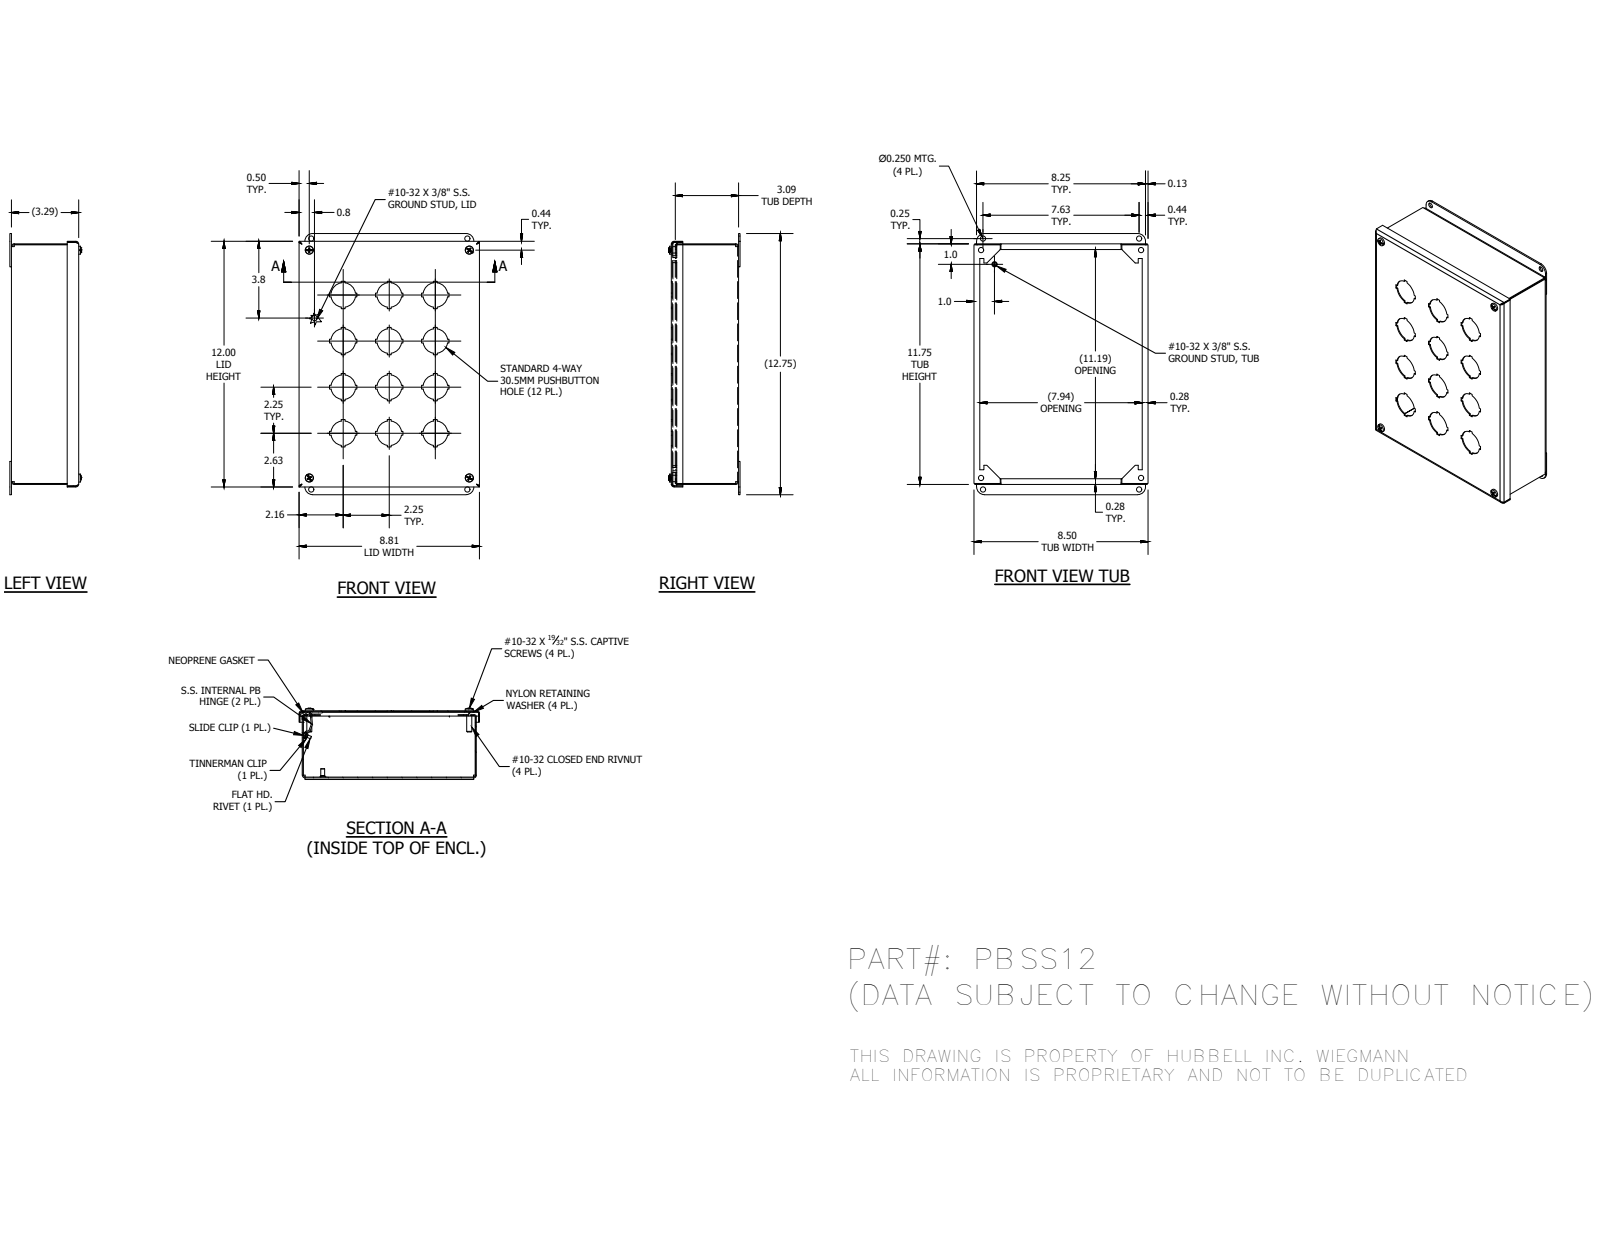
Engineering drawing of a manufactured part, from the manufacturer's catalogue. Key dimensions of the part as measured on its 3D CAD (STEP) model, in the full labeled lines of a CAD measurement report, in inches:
Part name (STEP PRODUCT): PBSS12LID; 37210; 39077; PBSS12BKP (+8 more)
STEP written by: Autodesk Inventor 2016 (AUTOMOTIVE_DESIGN)
Units: inches
Bodies: 25 solids, 841 faces (553 planar, 180 cylindrical, 108 other)
Overall size (bounding box): 12.75 × 8.813 × 3.481
Volume: 22.16 in³ · Surface area: 826.6 in²
Round holes (diameter × count): ⌀1.2 ×12, ⌀0.156 ×4, ⌀0.196 ×4, ⌀0.25 ×4, ⌀0.257 ×4, ⌀0.278 ×4, ⌀0.281 ×4, ⌀0.313 ×4, ⌀0.133 ×2, ⌀0.14 ×2
Round bosses / shafts (diameter × count): ⌀0.453 ×4, ⌀0.406 ×4, ⌀0.248 ×4, ⌀0.167 ×4, ⌀0.25 ×3, ⌀0.19 ×2, ⌀0.125 ×1
Partial cylindrical surfaces — rounded edges, fillets, slot ends (radius × count): R0.094 ×8, R0.139 ×8, R0.188 ×6, R0.063 ×4, R0.089 ×4, R0.09 ×4, R0.375 ×4, R0.031 ×3
Main face-to-face distances: 0.045, 0.045, 3.195, 3.24, 3.24, 3.285, 11.705, 8.455, 8.5, 8.41
Hole centre spacings: 2.25, 5.031, 3.182, 4.5, 0.019, 3.163, 5.239, 6.364
